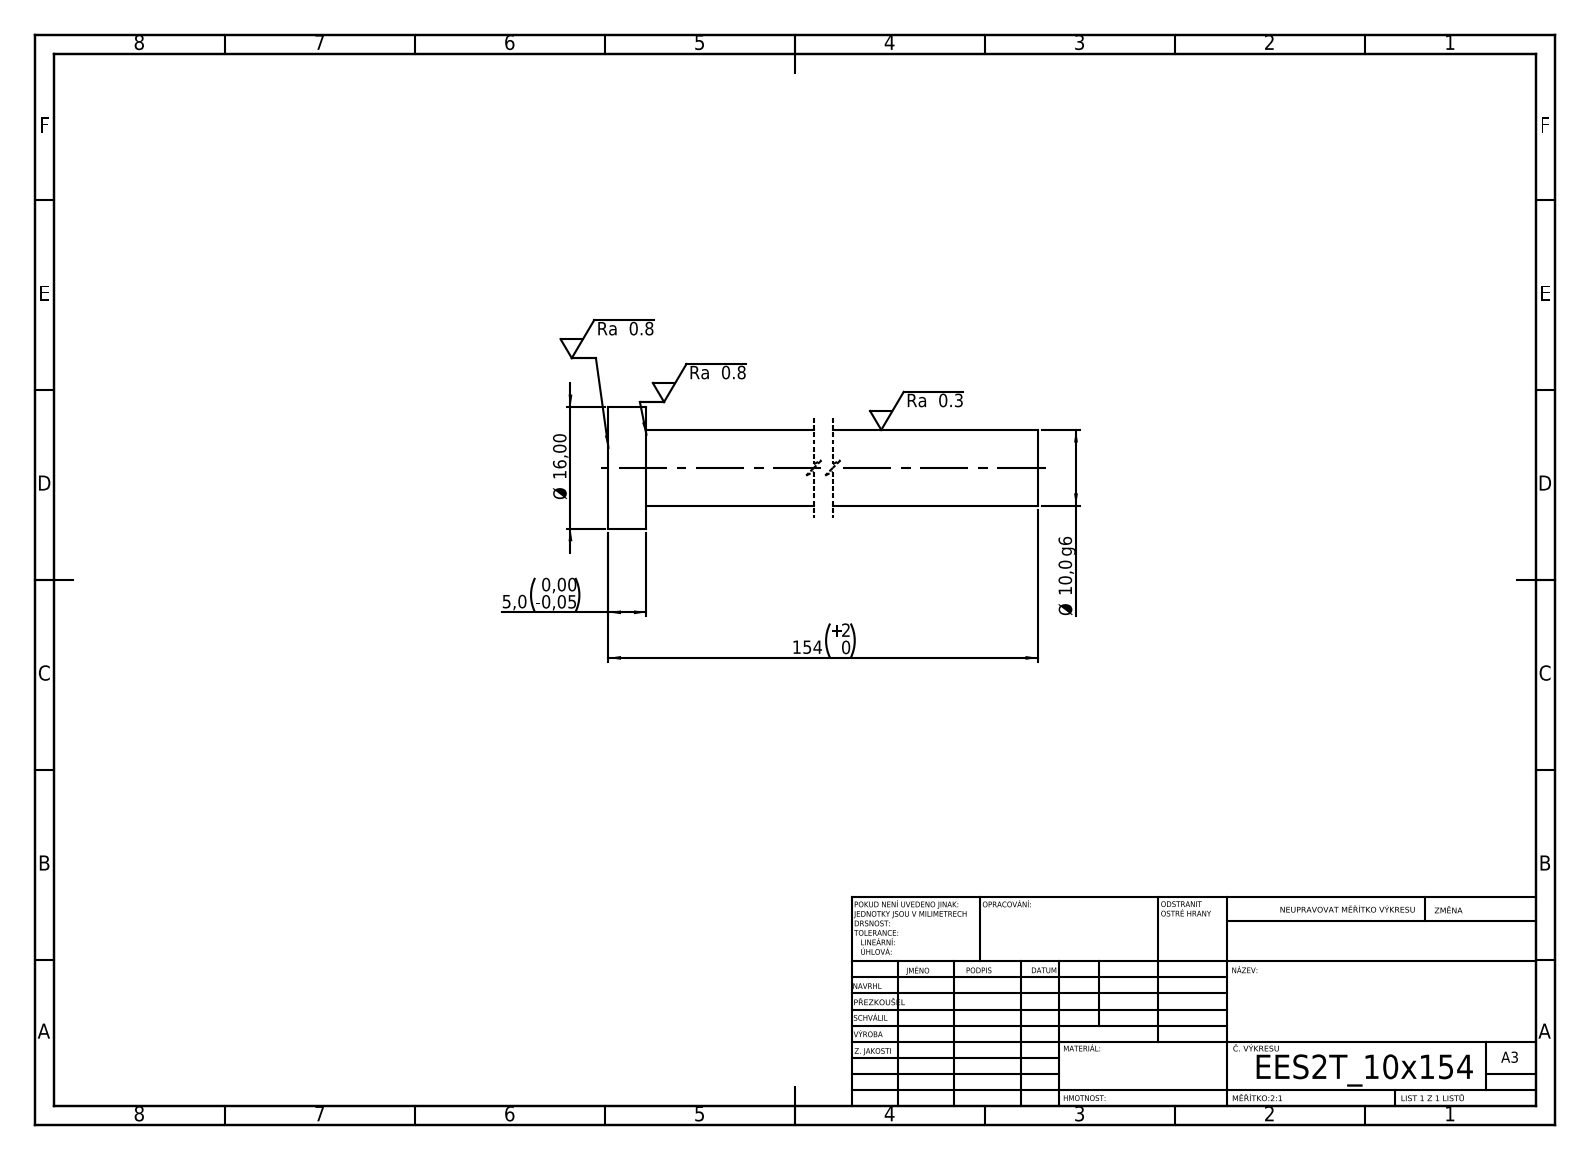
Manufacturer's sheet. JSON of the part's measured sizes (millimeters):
{"step_written_by": "SolidWorks 2019 (CONFIG_CONTROL_DESIGN)", "units": "millimeters", "bodies": {"solids": 1, "faces": 7, "planar": 3, "cylindrical": 4, "other": 0}, "overall_size": [154, 16, 16], "volume_mm3": 12708, "surface_area_mm2": 5334, "round_bosses_or_shafts": [[16, 1], [10, 1]], "face_to_face_distances": [5, 154, 149]}
